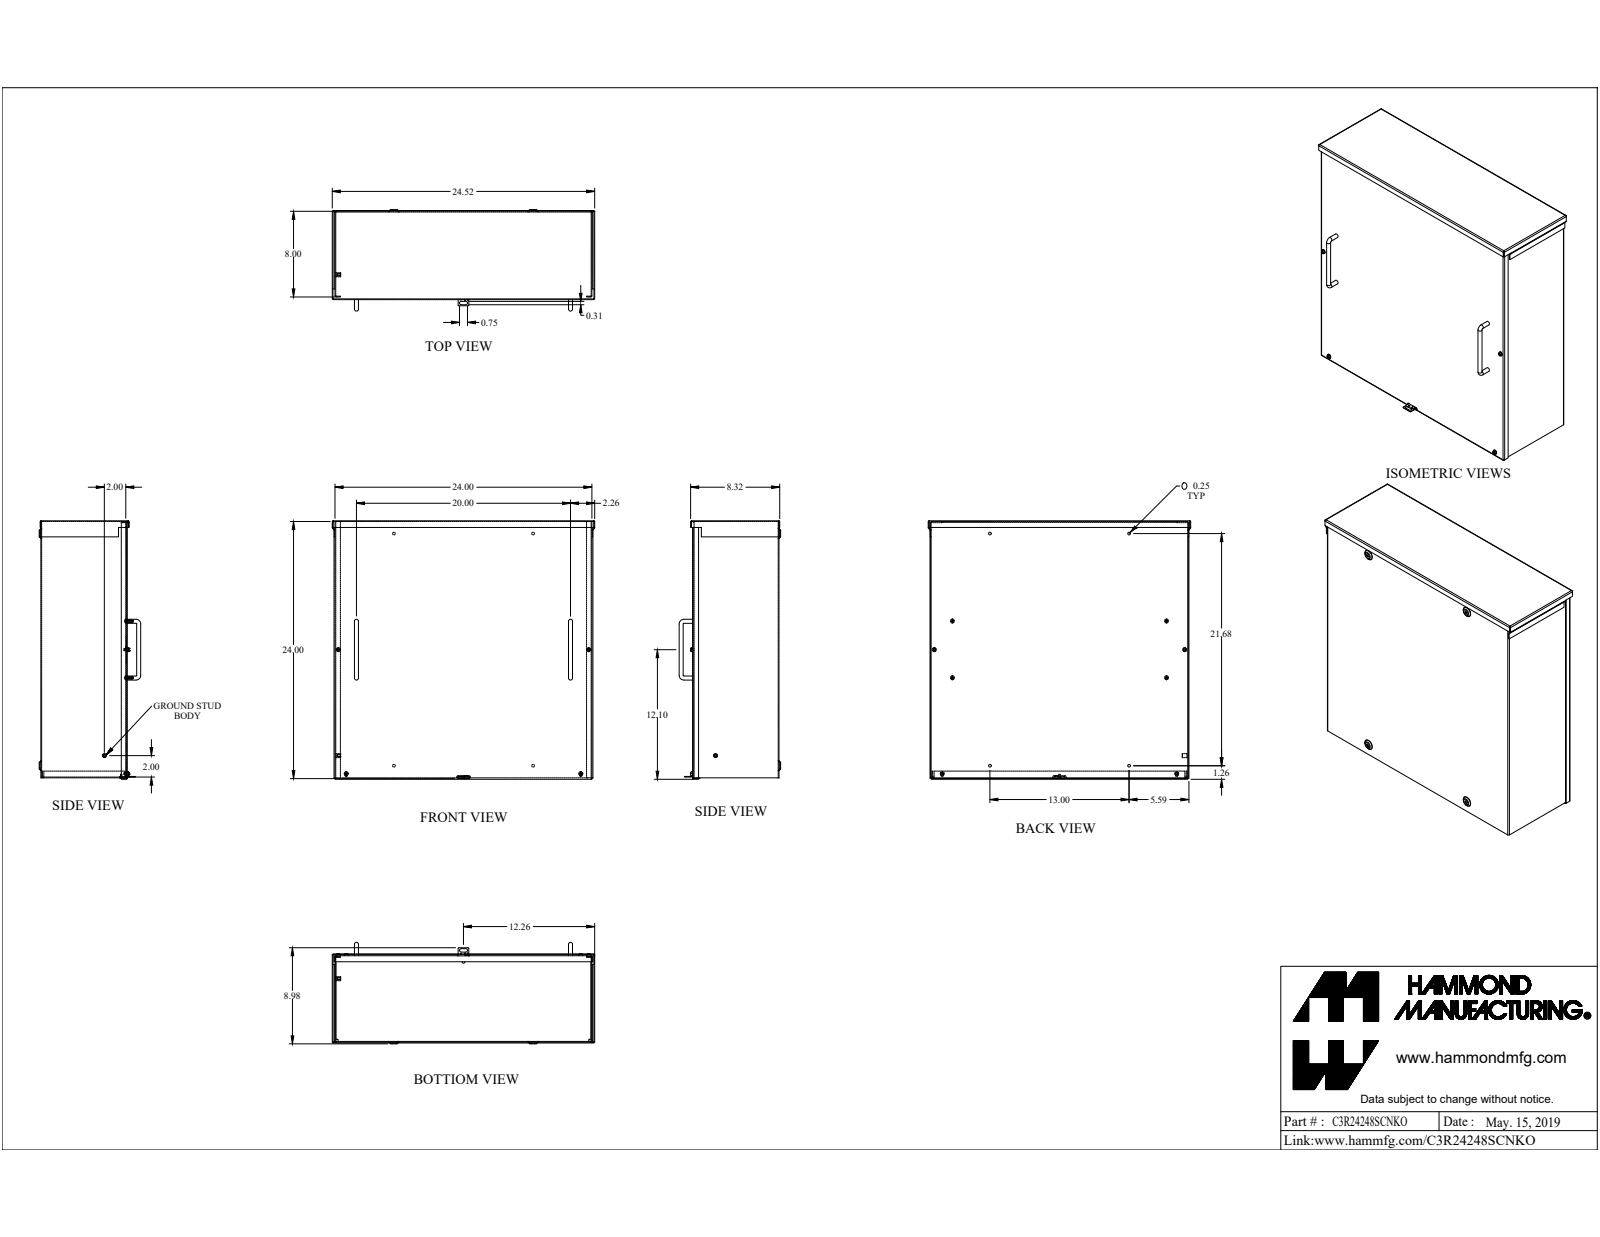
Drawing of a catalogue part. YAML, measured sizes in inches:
part_name: "C3R24248SCNKO"
step_written_by: "SolidWorks 2019 (AUTOMOTIVE_DESIGN)"
units: inches
bodies: {solids: 17, faces: 453, planar: 287, cylindrical: 106, other: 60}
overall_size: [24.519, 24.135, 9.478]
volume: 148.7
surface_area: 4183
round_holes:
  - {diameter: 0.156, count: 5}
  - {diameter: 0.17, count: 4}
  - {diameter: 0.203, count: 4}
  - {diameter: 0.25, count: 4}
  - {diameter: 0.125, count: 1}
  - {diameter: 0.137, count: 1}
round_bosses_or_shafts:
  - {diameter: 0.375, count: 9}
  - {diameter: 0.19, count: 8}
  - {diameter: 0.367, count: 4}
  - {diameter: 0.375, count: 2}
  - {diameter: 0.125, count: 1}
partial_cylinders:
  - {radius: 0.036, count: 20}
  - {radius: 0.108, count: 20}
  - {radius: 0.109, count: 8}
  - {radius: 0.125, count: 8}
  - {radius: 0.156, count: 2}
  - {radius: 0.029, count: 1}
  - {radius: 0.086, count: 1}
face_to_face_distances: [0.072, 8, 7.928, 8.072, 23.928, 24, 0.072, 23.856, 23.856, 23.928]
hole_center_spacings: [20, 0.024, 3.146, 5.3, 8.906, 12.02, 13.936, 18.42]
